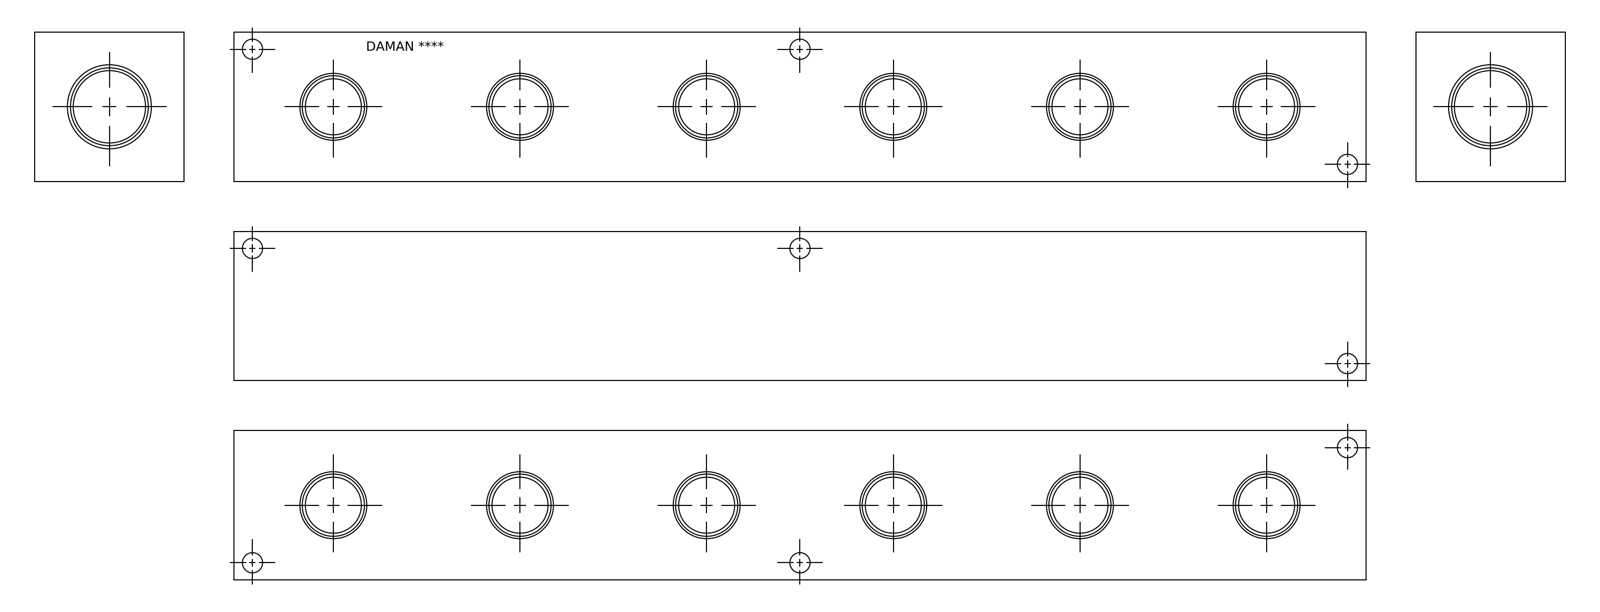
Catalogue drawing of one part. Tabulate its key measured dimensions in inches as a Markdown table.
| quantity | value |
| --- | --- |
| part name | Part_AH1800616P_3D |
| STEP written by | Autodesk Inventor 2019 (AUTOMOTIVE_DESIGN) |
| units | inches |
| bodies | 1 solid, 389 faces (236 planar, 40 cylindrical, 113 other) |
| overall size | 22.75 × 3 × 3 |
| volume | 184.5 in³ |
| surface area | 360.7 in² |
| round holes (diameter × count) | 0.406 × 6, 1.125 × 6, 1.327 × 6, 1.453 × 1, 1.672 × 1 |
| main face-to-face distances | 3, 22.75, 0.748, 2.252, 1.504, 0.768, 21.982, 21.214, 2.961, 2.213 |
| hole center spacings | 3.75, 7.5, 11.25, 11, 15, 22.121, 1.994, 1.994 |
